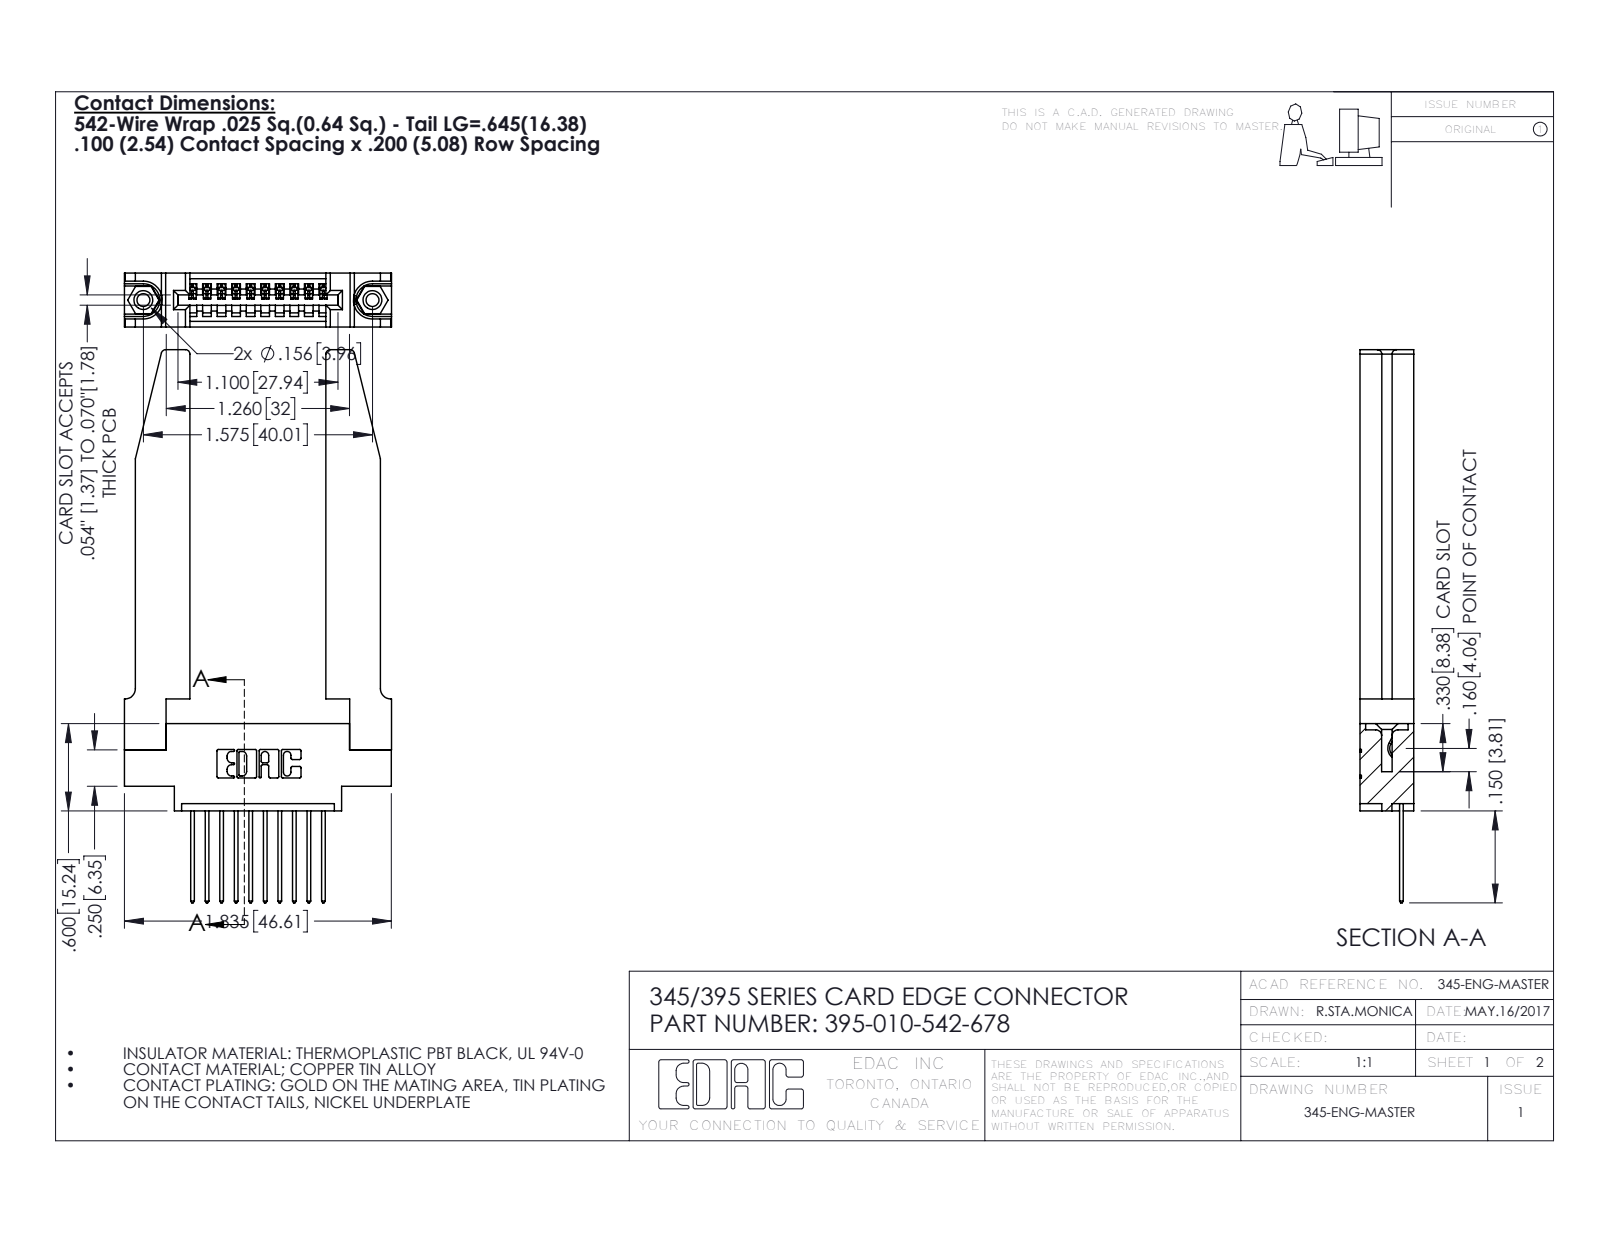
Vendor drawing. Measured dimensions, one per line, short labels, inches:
name: 345-292-001_345-293-142; 345 Part_0.170 Offset - 0.156 Dia-TH; 395-010-542-678; 345-220-078_345-220-078 (+1 more)
written by: SolidWorks 2016 (CONFIG_CONTROL_DESIGN)
unit: in
bodies: 15 solids, 944 faces (626 planar, 266 cylindrical, 52 other)
size: 3.802 × 1.836 × 0.37
volume: 0.723 in³; area: 18.75 in²
holes: 2× ⌀0.089, 2× ⌀0.125, 2× ⌀0.156, 1× ⌀0.064
bosses: 2× ⌀0.155
rounds: 22× R0.01, 20× R0.006, 20× R0.01, 8× R0.03, 6× R0.007, 6× R0.031, 3× R0.026, 2× R0.031
face distances: 0.37, 0.072, 0.298, 0.15, 0.148, 0.22, 0.077, 0.935, 0.098, 0.272
hole spacings: 0.27, 1.344, 1.575
